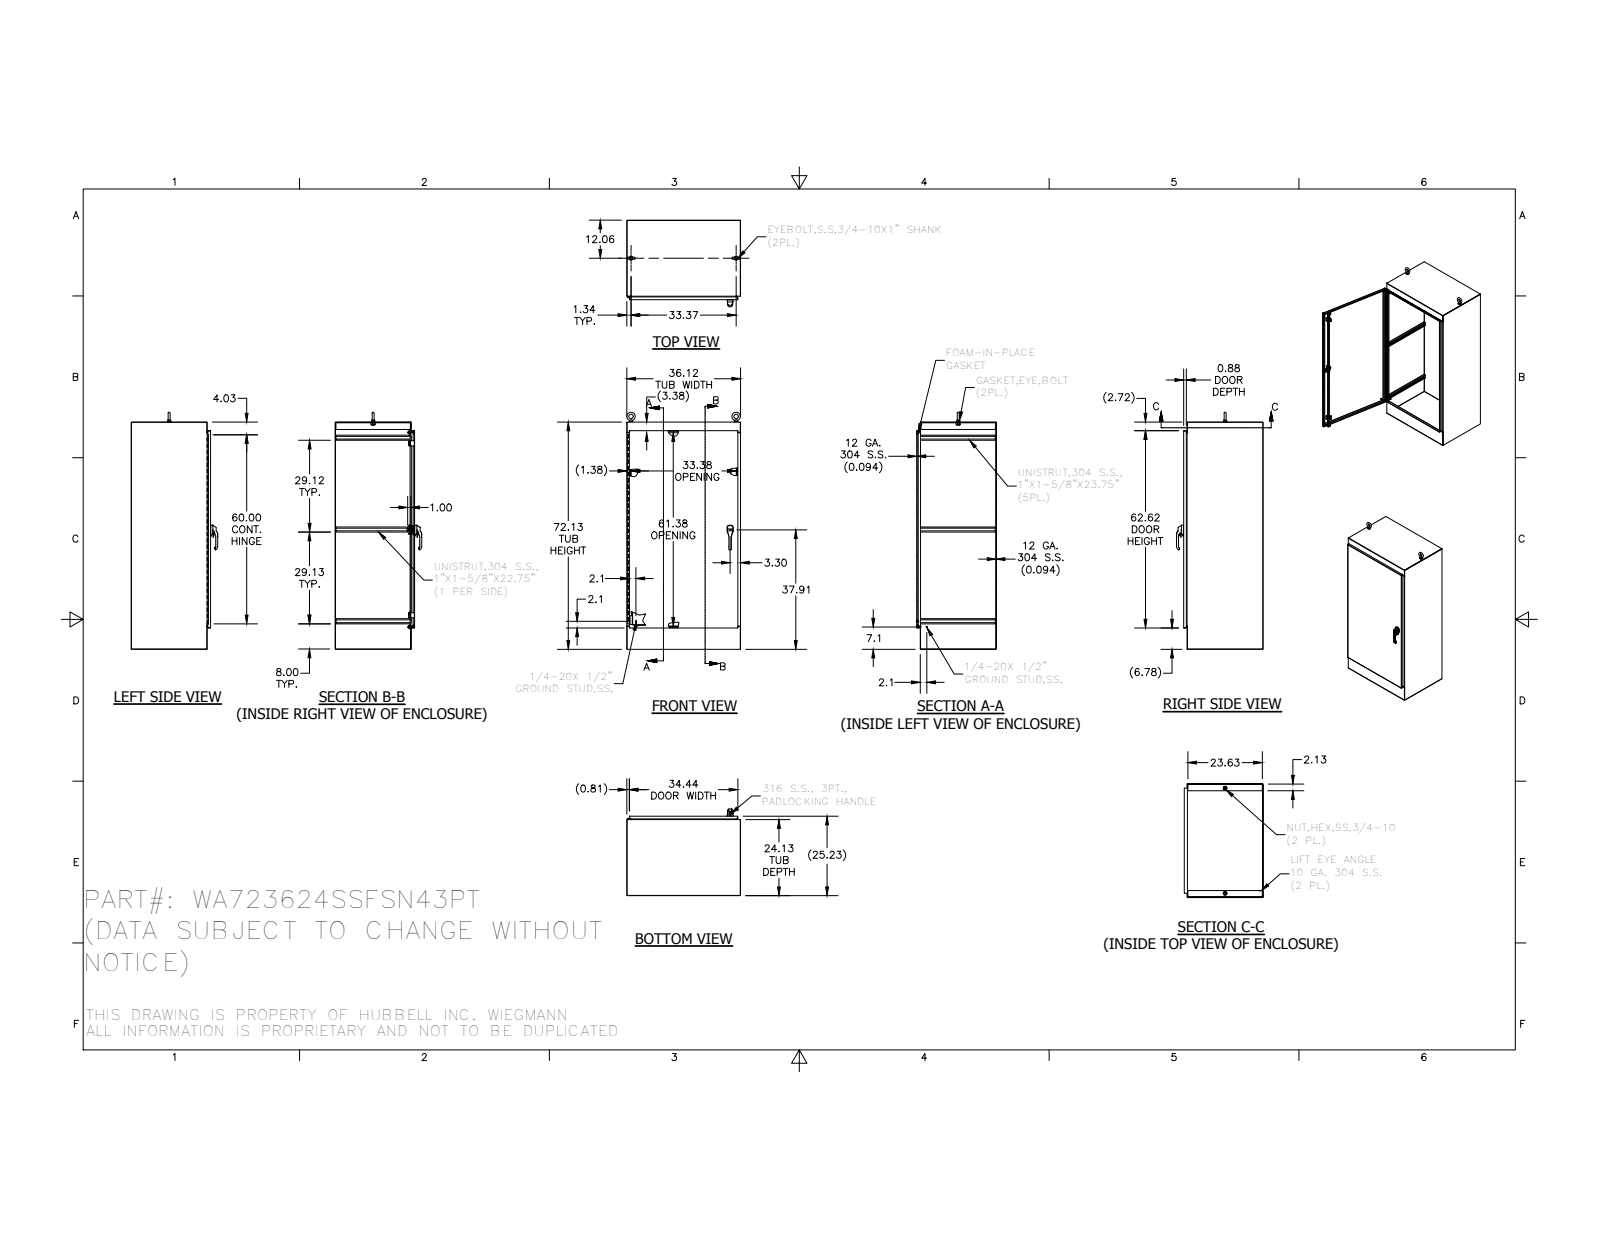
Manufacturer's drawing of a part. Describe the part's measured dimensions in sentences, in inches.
The part is named "328131T-60; HFW32451; 1000-277-01; WA7224SSFSN43PT-LS (+8 more)". Its 3-D file was written by "SolidWorks 2014 (AUTOMOTIVE_DESIGN)". It is 66 solids with 3475 faces: 1228 planar, 1307 cylindrical and 940 other. Overall it measures 75.248 by 36.125 by 27.476 inches. Its volume is 1 178 cubic inches and its surface area 24 431 square inches. Round holes: 8 of diameter 0.262, 8 of diameter 0.375, 4 of diameter 0.187, 3 of diameter 0.213, 3 of diameter 0.25, 3 of diameter 0.28, 2 of diameter 0.165, 2 of diameter 0.241, 2 of diameter 0.252, 2 of diameter 0.315, 2 of diameter 0.4, 2 of diameter 0.402. Round bosses or shafts: 3 of diameter 1, 3 of diameter 0.236, 2 of diameter 1.25, 2 of diameter 1.12, 2 of diameter 0.75, 2 of diameter 0.563, 2 of diameter 0.533, 2 of diameter 0.531. Partial cylindrical surfaces (rounded edges, fillets, slot ends): 180 of radius 0.02, 107 of radius 0.012, 26 of radius 0.125, 23 of radius 0.019, 19 of radius 0.05, 17 of radius 0.031, 14 of radius 0.079, 13 of radius 0.125. The main face-to-face distances are 0.094, 25.133, 36.031, 25.039, 25.227, 35.937, 36.125, 72.031, 24.031, 1.102. The hole center spacings are 6.667, 20, 0.38, 0.76, 1.102, 1.714, 2.763, 13.333.
